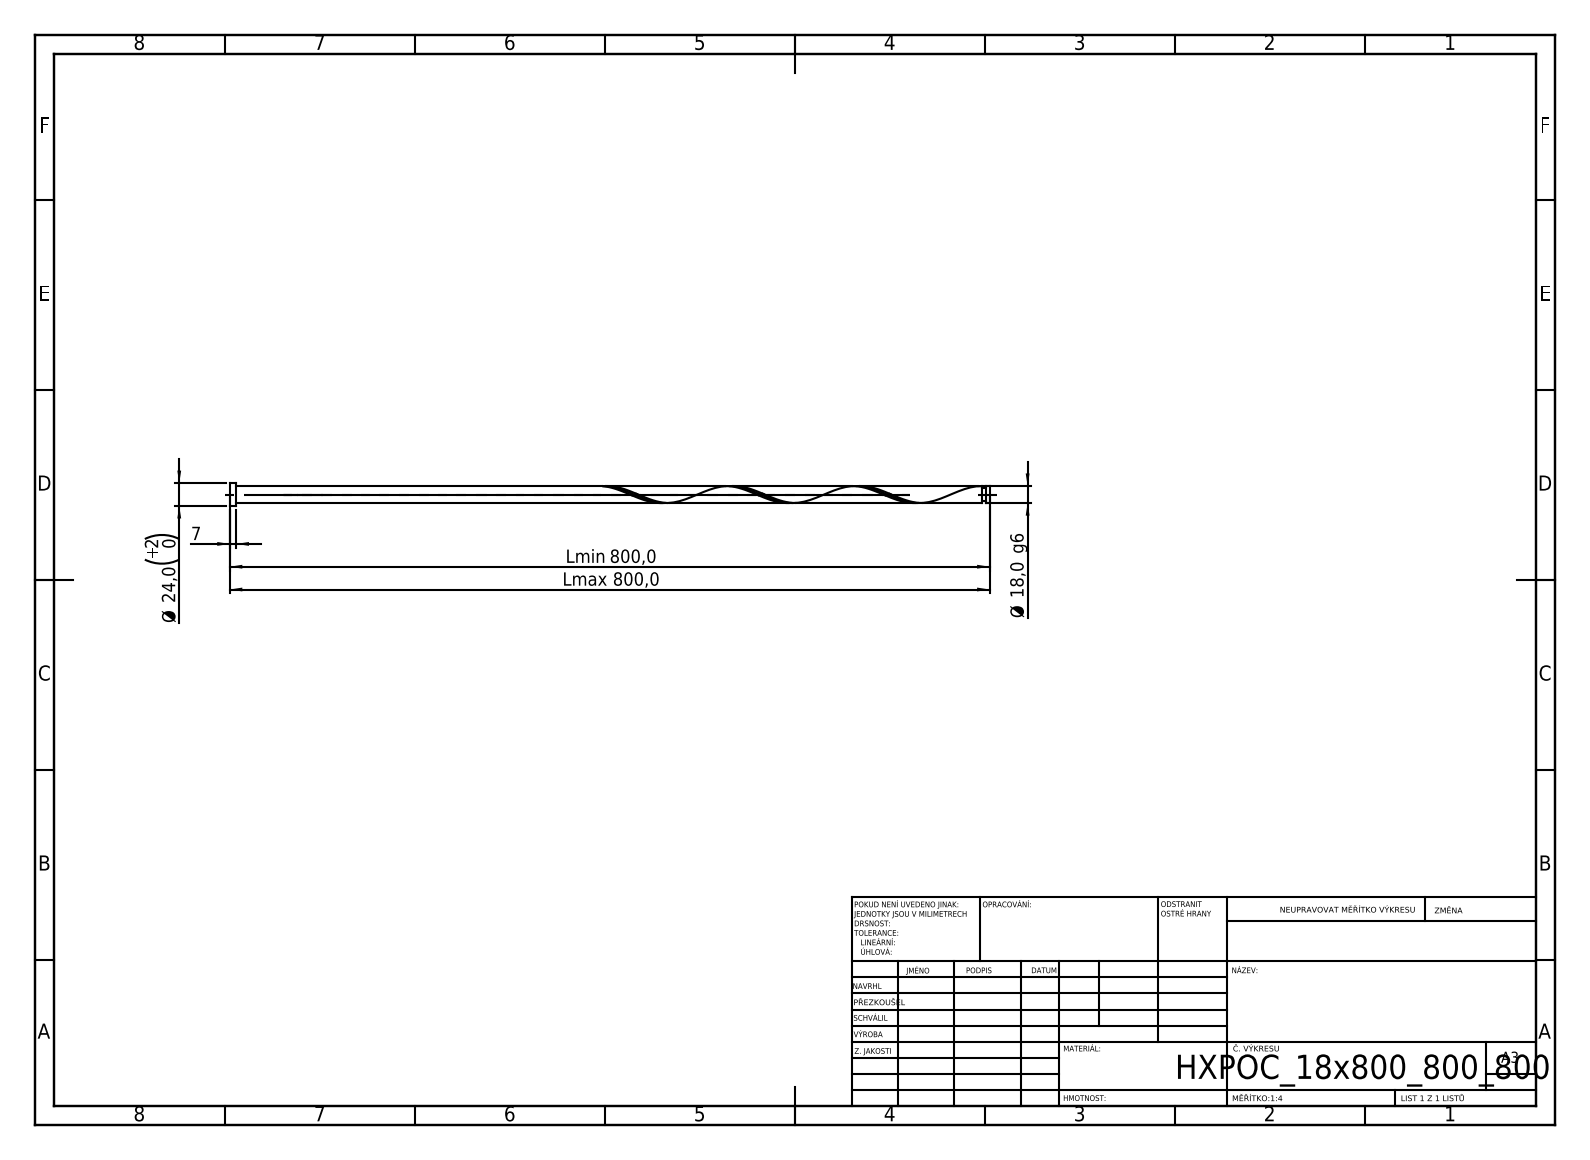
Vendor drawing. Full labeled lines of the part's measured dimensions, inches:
STEP written by: SolidWorks 2019 (CONFIG_CONTROL_DESIGN)
Units: inches
Bodies: 1 solid, 21 faces (6 planar, 14 cylindrical, 1 other)
Overall size (bounding box): 31.496 × 0.945 × 0.945
Volume: 12.37 in³ · Surface area: 73.13 in²
Round bosses / shafts (diameter × count): ⌀0.945 ×1, ⌀0.709 ×1, ⌀0.567 ×1
Main face-to-face distances: 31.496, 0.276, 31.22, 31.335, 31.06, 0.161, 31.194, 30.918, 0.142, 0.302
